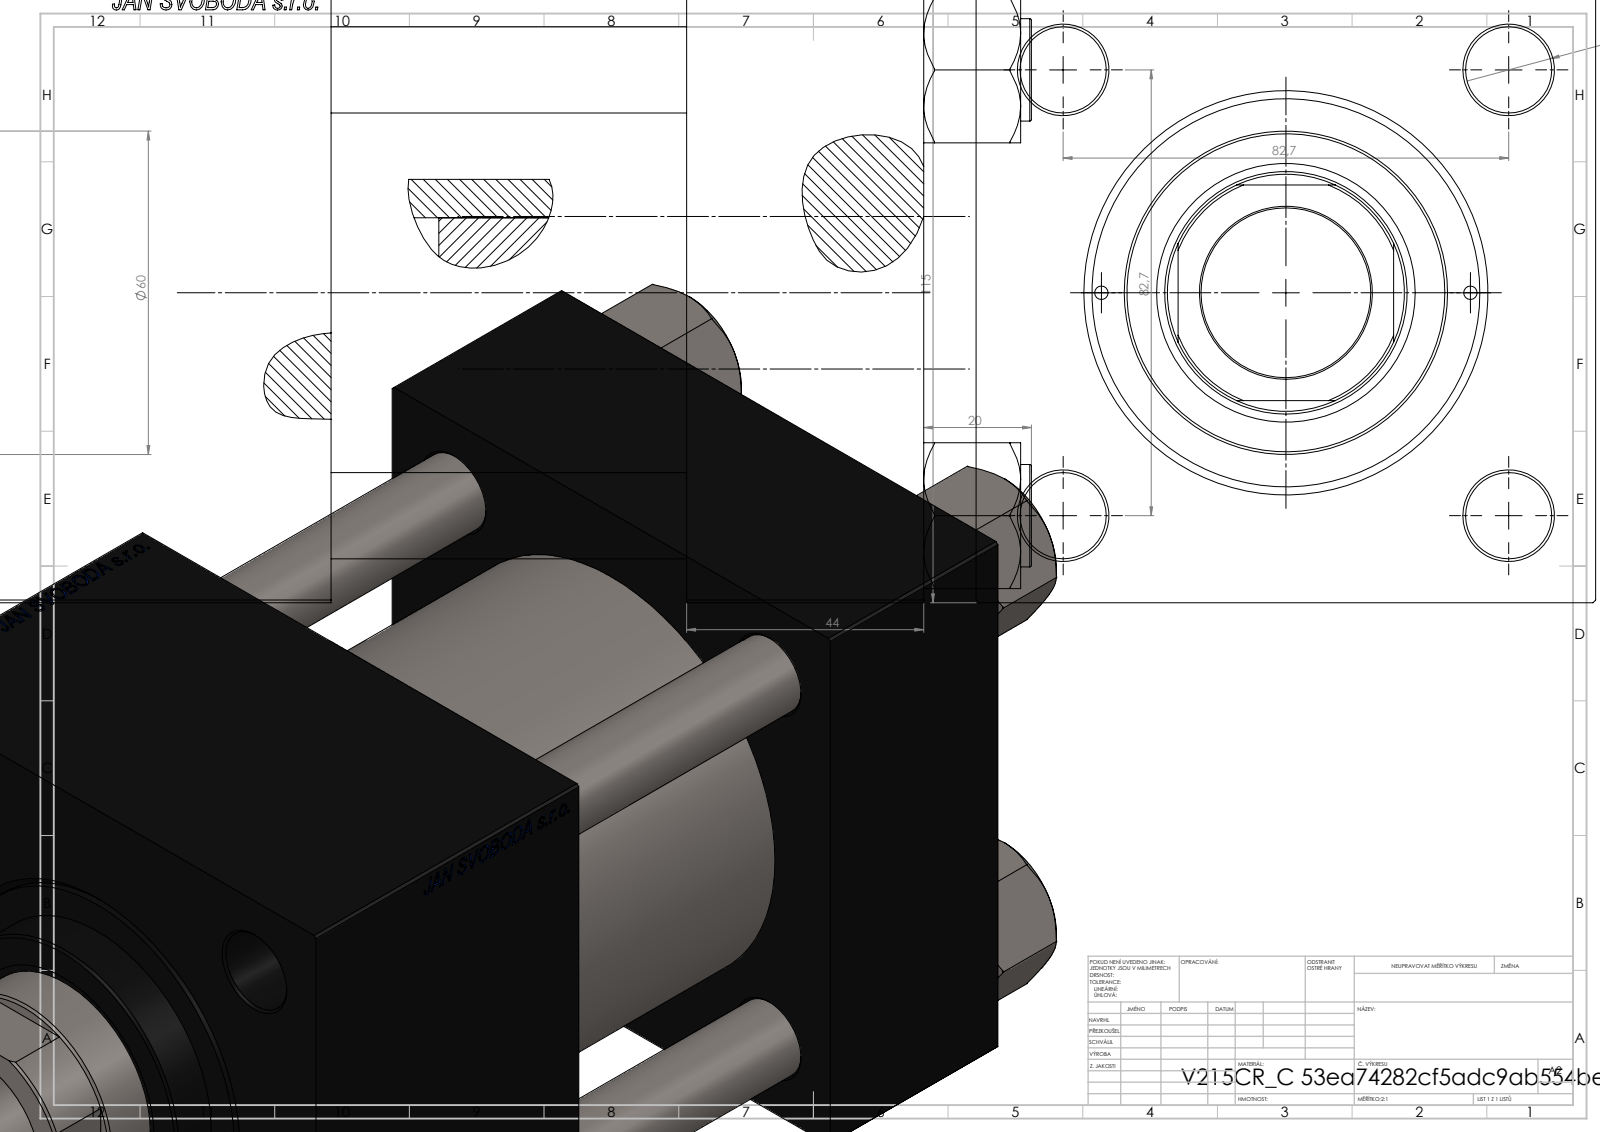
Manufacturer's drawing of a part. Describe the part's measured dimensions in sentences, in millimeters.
The part is named "V215CR_C_TYCINKA; V215CR_VCP_C; NUT_M5_C; V215_VC_A (+1 more)". Its 3-D file was written by "SolidWorks 2019 (CONFIG_CONTROL_DESIGN)". It is 11 solids with 1202 faces: 576 planar, 90 cylindrical and 536 other. Overall it measures 230 by 115 by 115 millimeters. Its volume is 1 819 000 cubic millimeters and its surface area 273 954 square millimeters. Round holes: 4 of diameter 16, 2 of diameter 2.5, 2 of diameter 7, 2 of diameter 26.44, 2 of diameter 35, 1 of diameter 31.5, 1 of diameter 45, 1 of diameter 48, 1 of diameter 61, 1 of diameter 72, 1 of diameter 80. Round bosses or shafts: 4 of diameter 19, 1 of diameter 86, 1 of diameter 60. Partial cylindrical surfaces (rounded edges, fillets, slot ends): 1 of radius 22. The main face-to-face distances are 115, 44, 110, 179, 135, 66, 69, 20, 150.3, 106.3. The hole center spacings are 41.96, 58.48, 82.7, 86.17, 34.25, 116.96, 68.5, 111.
